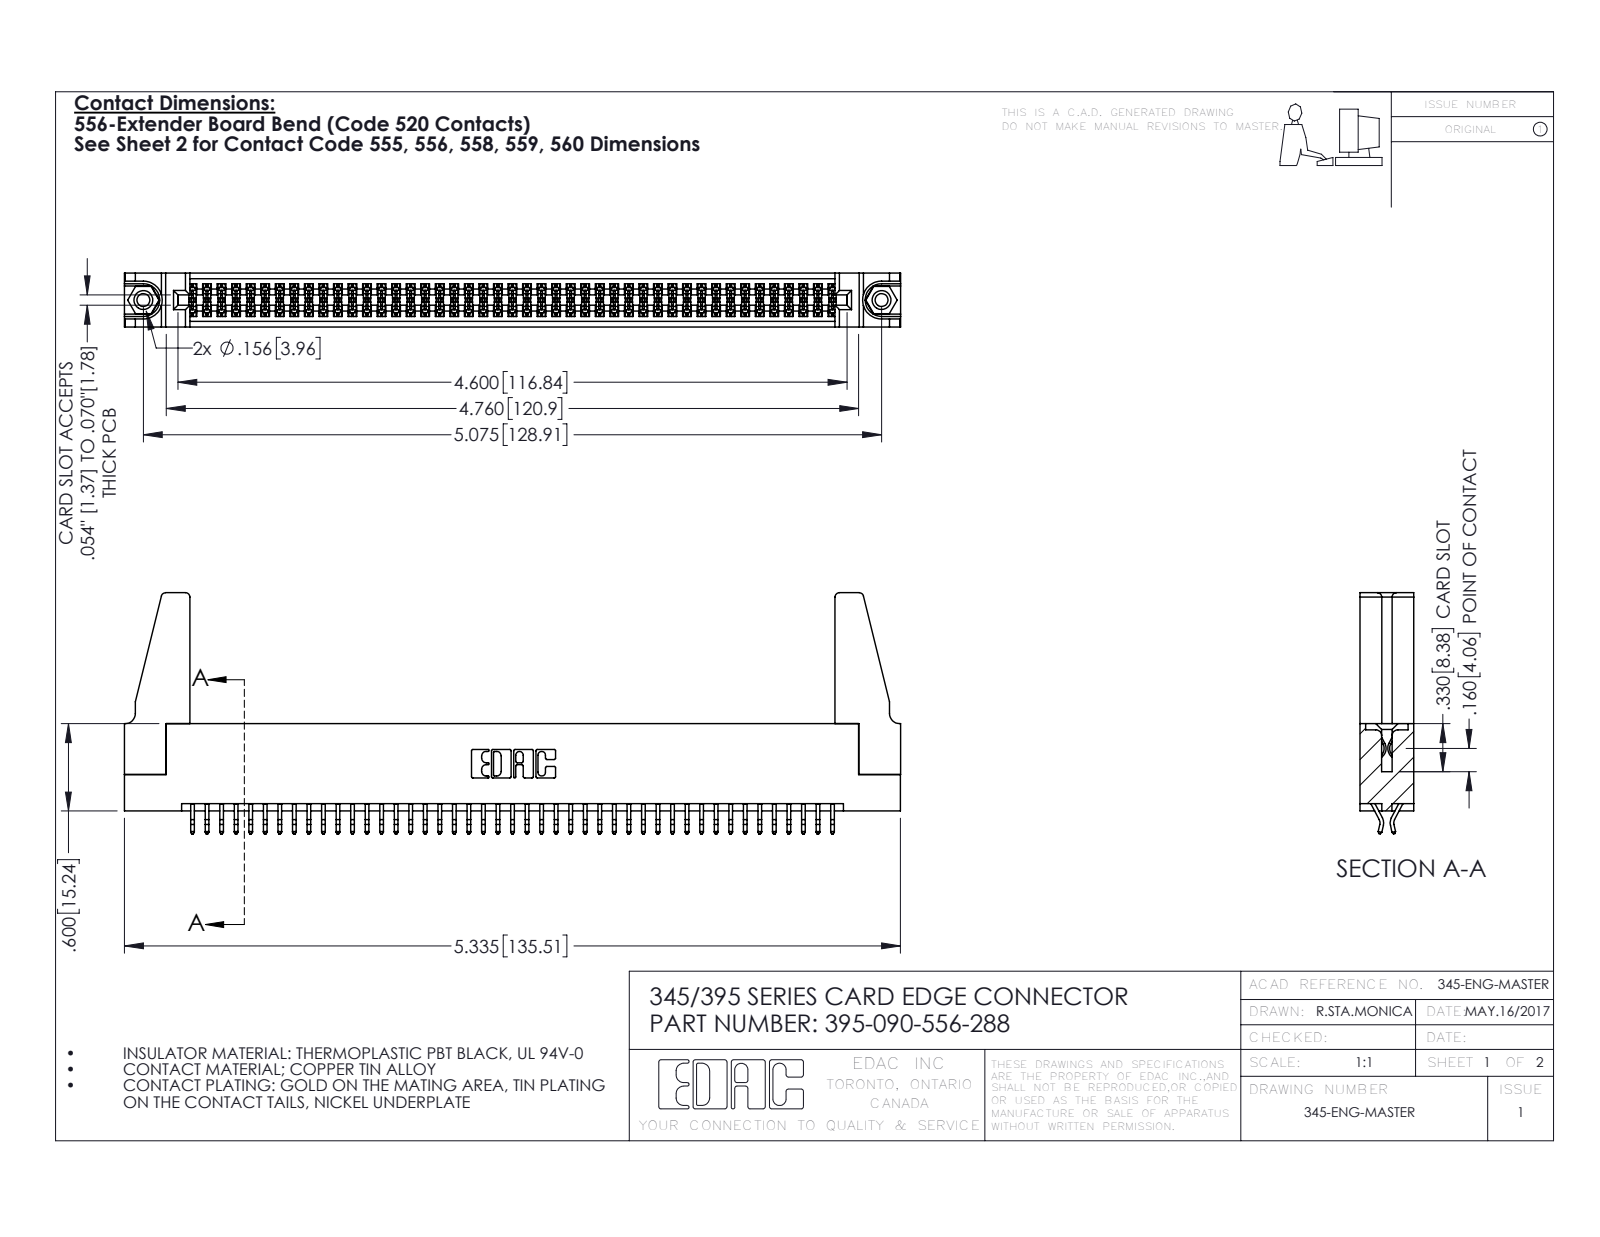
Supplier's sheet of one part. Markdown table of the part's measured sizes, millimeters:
| quantity | value |
| --- | --- |
| part name | 395-090-556-288; 345-220-078_345-220-088; 345-292-001_556 Tail; 345-250-001_345-250-001-102 (+1 more) |
| STEP written by | SolidWorks 2016 (CONFIG_CONTROL_DESIGN) |
| units | millimeters |
| bodies | 95 solids, 5290 faces (3482 planar, 1792 cylindrical, 16 other) |
| overall size | 135.5 × 42.1 × 9.4 |
| volume | 16 440 mm³ |
| surface area | 22 600 mm² |
| round holes (diameter × count) | 2.3 × 2, 3.2 × 2, 4 × 2, 1.6 × 1 |
| round bosses / shafts (diameter × count) | 3.9 × 2 |
| partial cylindrical surfaces (radius × count) | 0.2 × 135, 0.3 × 22, 0.8 × 8, 0.2 × 6, 0.8 × 6, 0.7 × 3, 0.3 × 2, 0.4 × 2 |
| main face-to-face distances | 1.8, 7.6, 9.4, 5.1, 0.6, 2.5, 6.9, 5.7, 4.4, 3.8 |
| hole center spacings | 6.9, 122.9, 128.9 |
